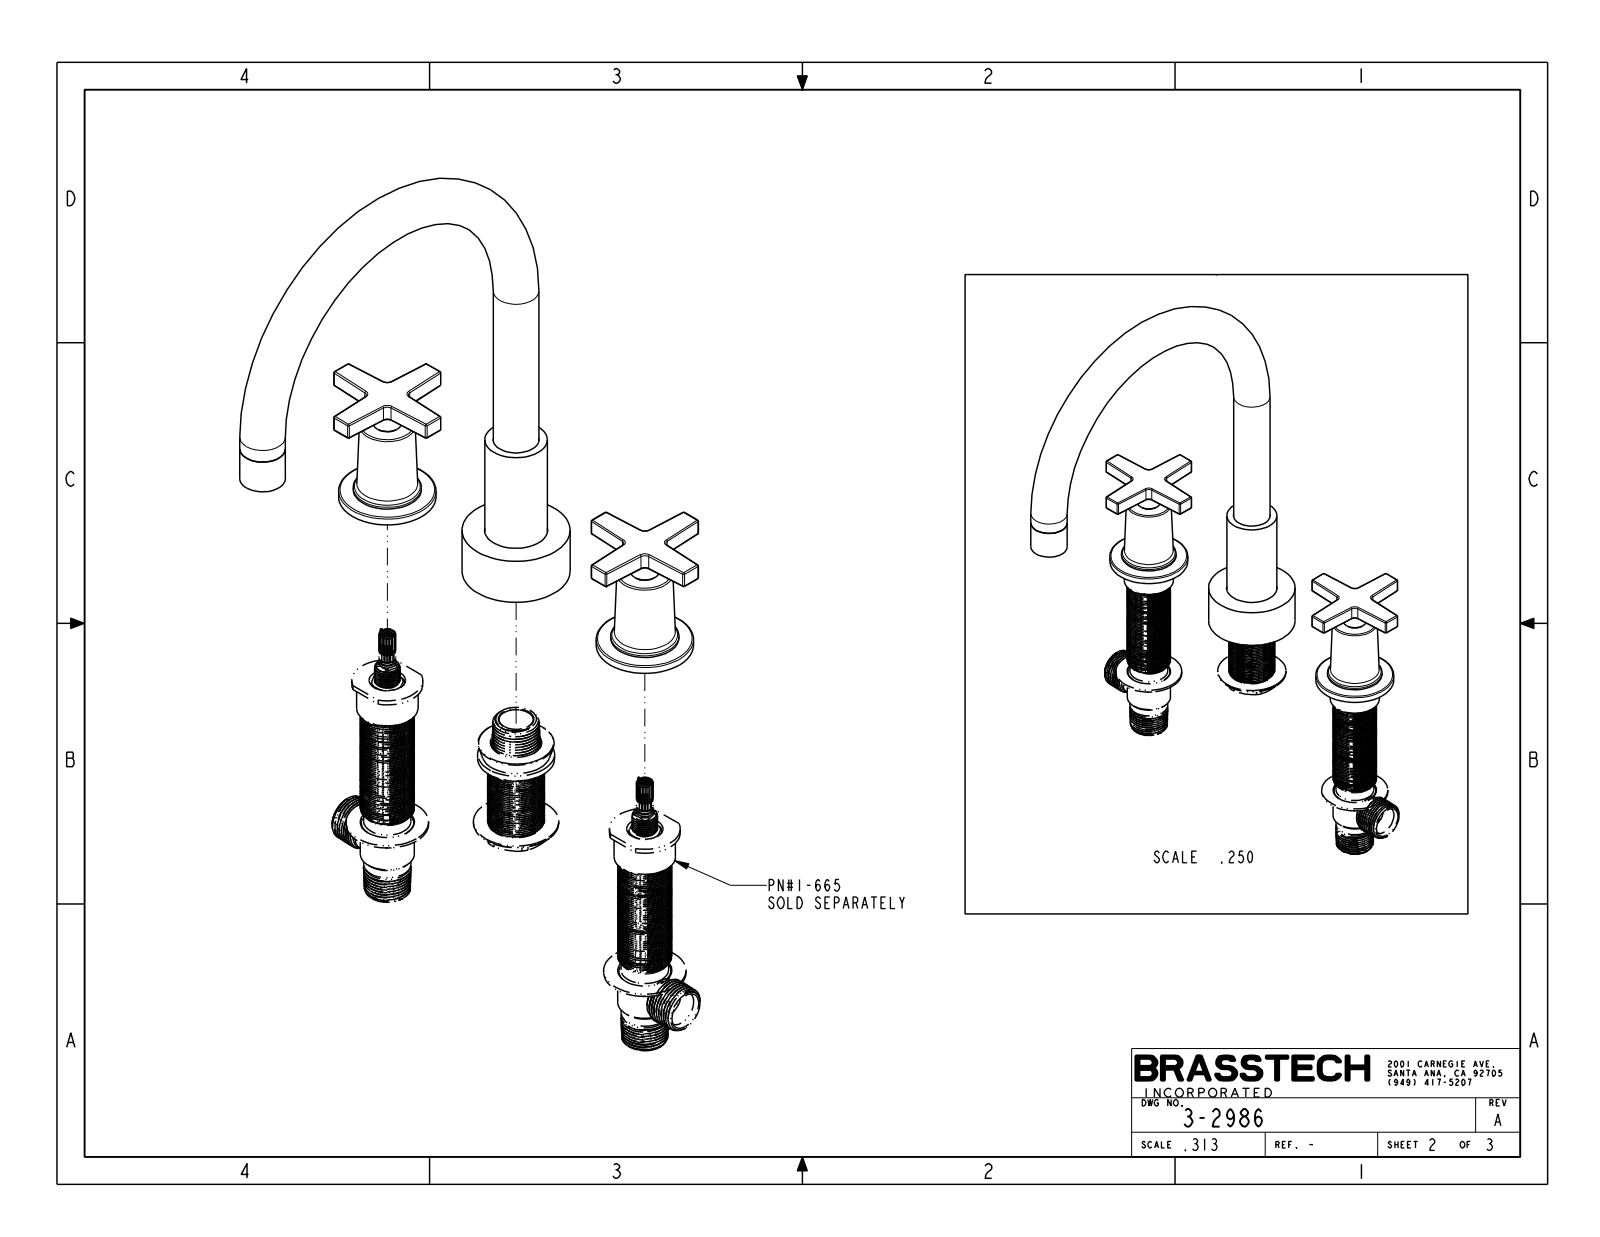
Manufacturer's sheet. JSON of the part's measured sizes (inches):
{"part_name": "3-2986", "step_written_by": "CREO PARAMETRIC BY PTC INC, 2018400 (CONFIG_CONTROL_DESIGN)", "units": "inches", "bodies": {"solids": 3, "faces": 216, "planar": 42, "cylindrical": 100, "other": 74}, "overall_size": [11.978, 10.886, 9.818], "volume_in3": 30.9, "surface_area_in2": 135.8, "round_bosses_or_shafts": [[2.2, 2], [1.5, 2], [1.275, 2], [1, 2], [0.625, 2], [0.525, 2], [2.375, 1], [1.375, 1]], "partial_cylinders_radius": [[0.03, 60], [0.125, 8]], "face_to_face_distances": [2.87, 0.187, 2.683, 2.495, 2.308, 0.375, 1.103, 0.916, 1.392, 1.767]}
